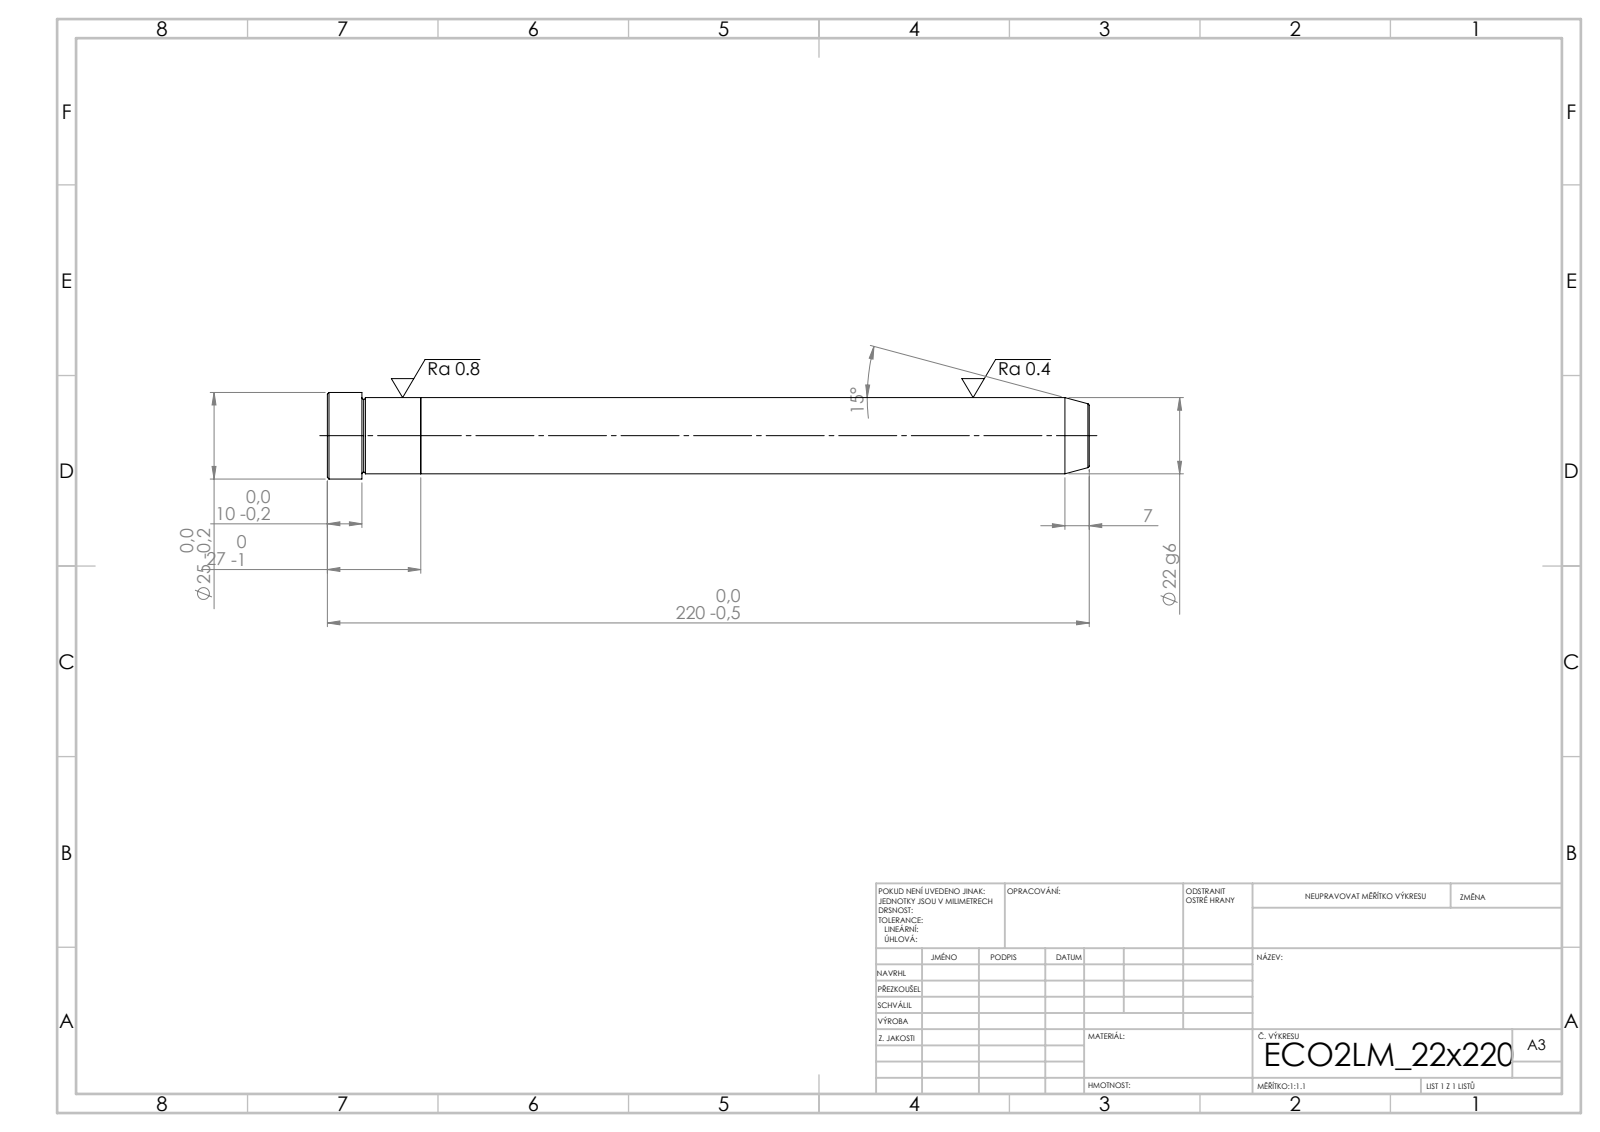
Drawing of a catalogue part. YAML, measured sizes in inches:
step_written_by: "SolidWorks 2019 (CONFIG_CONTROL_DESIGN)"
units: inches
bodies: {solids: 2, faces: 21, planar: 5, cylindrical: 6, other: 10}
overall_size: [8.661, 0.984, 0.984]
volume: 5.143
surface_area: 26.2
round_bosses_or_shafts:
  - {diameter: 0.984, count: 1}
  - {diameter: 0.866, count: 1}
face_to_face_distances: [1.063, 7.598, 8.661, 8.268, 0.669, 0.394]
